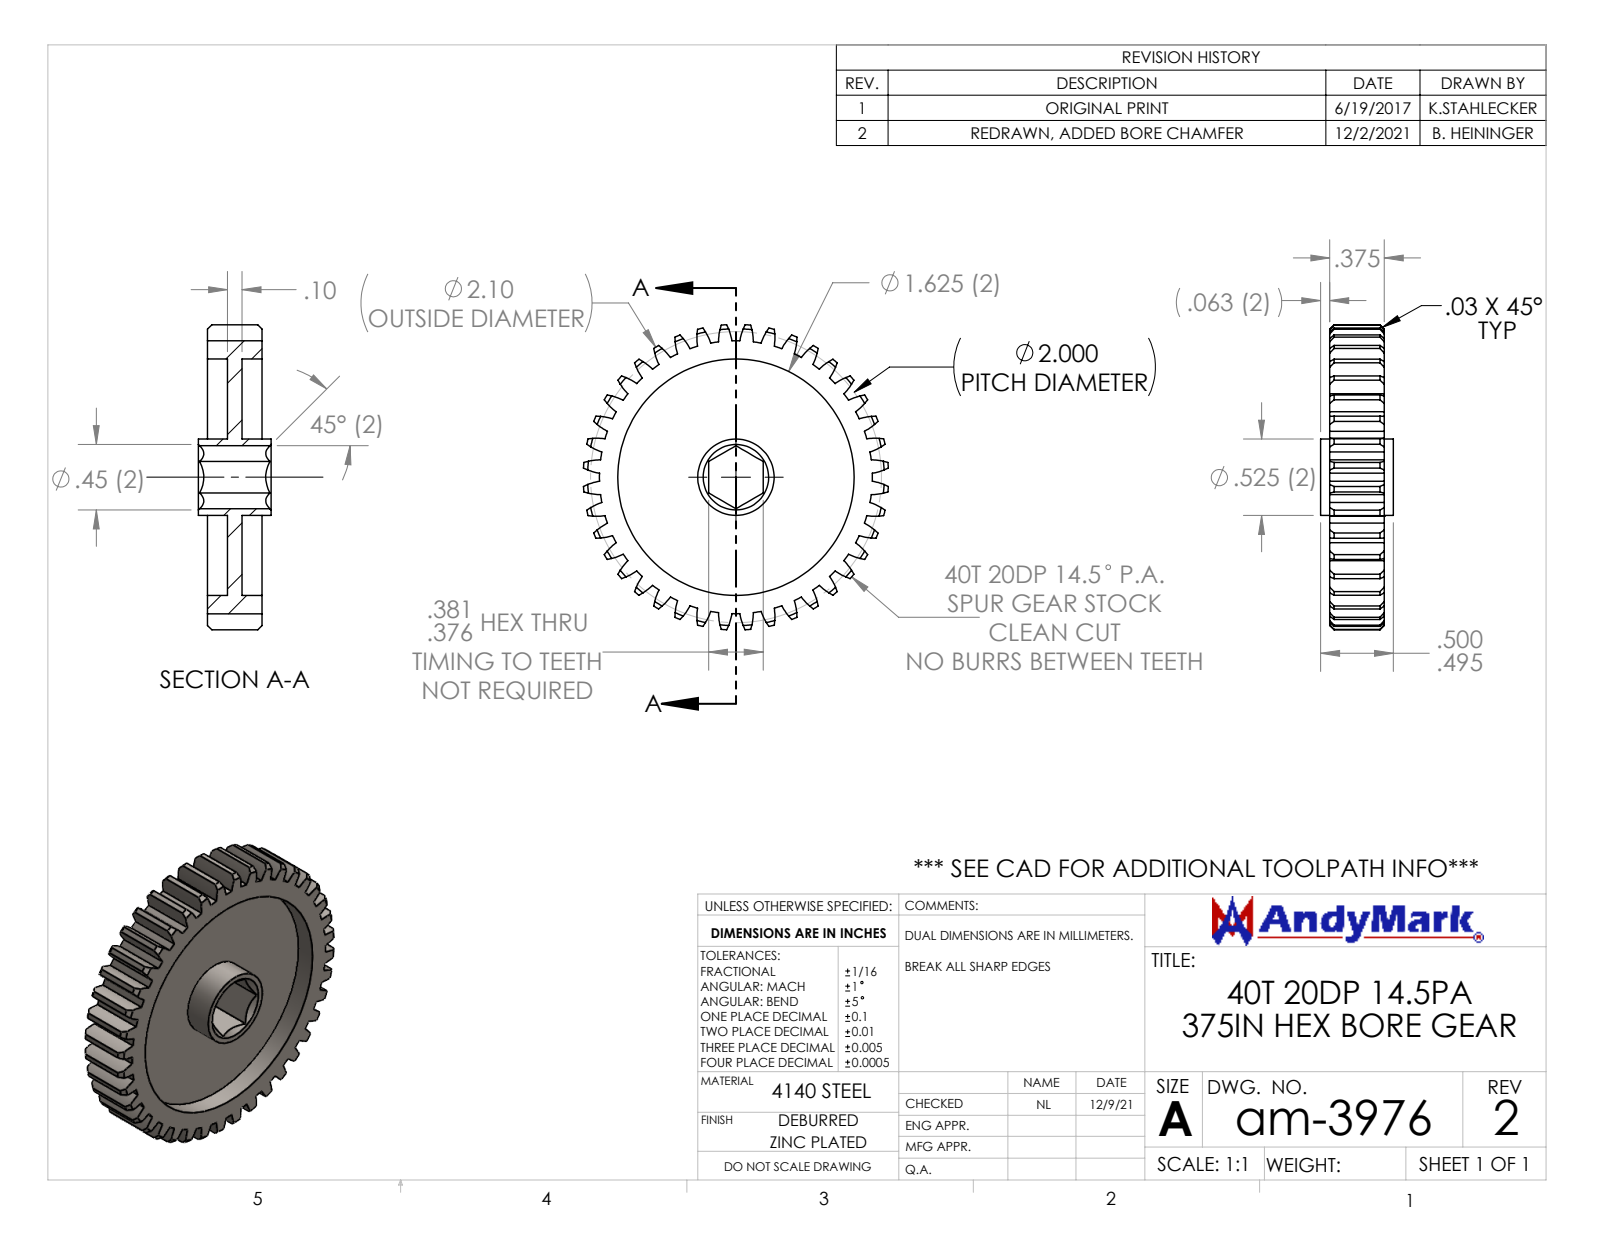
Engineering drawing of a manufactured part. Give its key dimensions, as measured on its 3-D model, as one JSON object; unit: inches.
{"part_name": "am-3976 40T 20DP 375hex 375 FW", "step_written_by": "SolidWorks 2021 (AUTOMOTIVE_DESIGN)", "units": "inches", "bodies": {"solids": 1, "faces": 267, "planar": 12, "cylindrical": 171, "other": 84}, "overall_size": [2.096, 2.096, 0.5], "volume_in3": 0.609, "surface_area_in2": 13.38, "round_holes": [[1.625, 1]], "round_bosses_or_shafts": [[0.525, 1]], "partial_cylinders_radius": [[0.4, 80], [0.938, 1], [1.05, 1]], "face_to_face_distances": [0.1, 0.137, 0.237, 0.375, 0.238, 0.138, 0.375, 0.2, 0.3, 0.063]}
